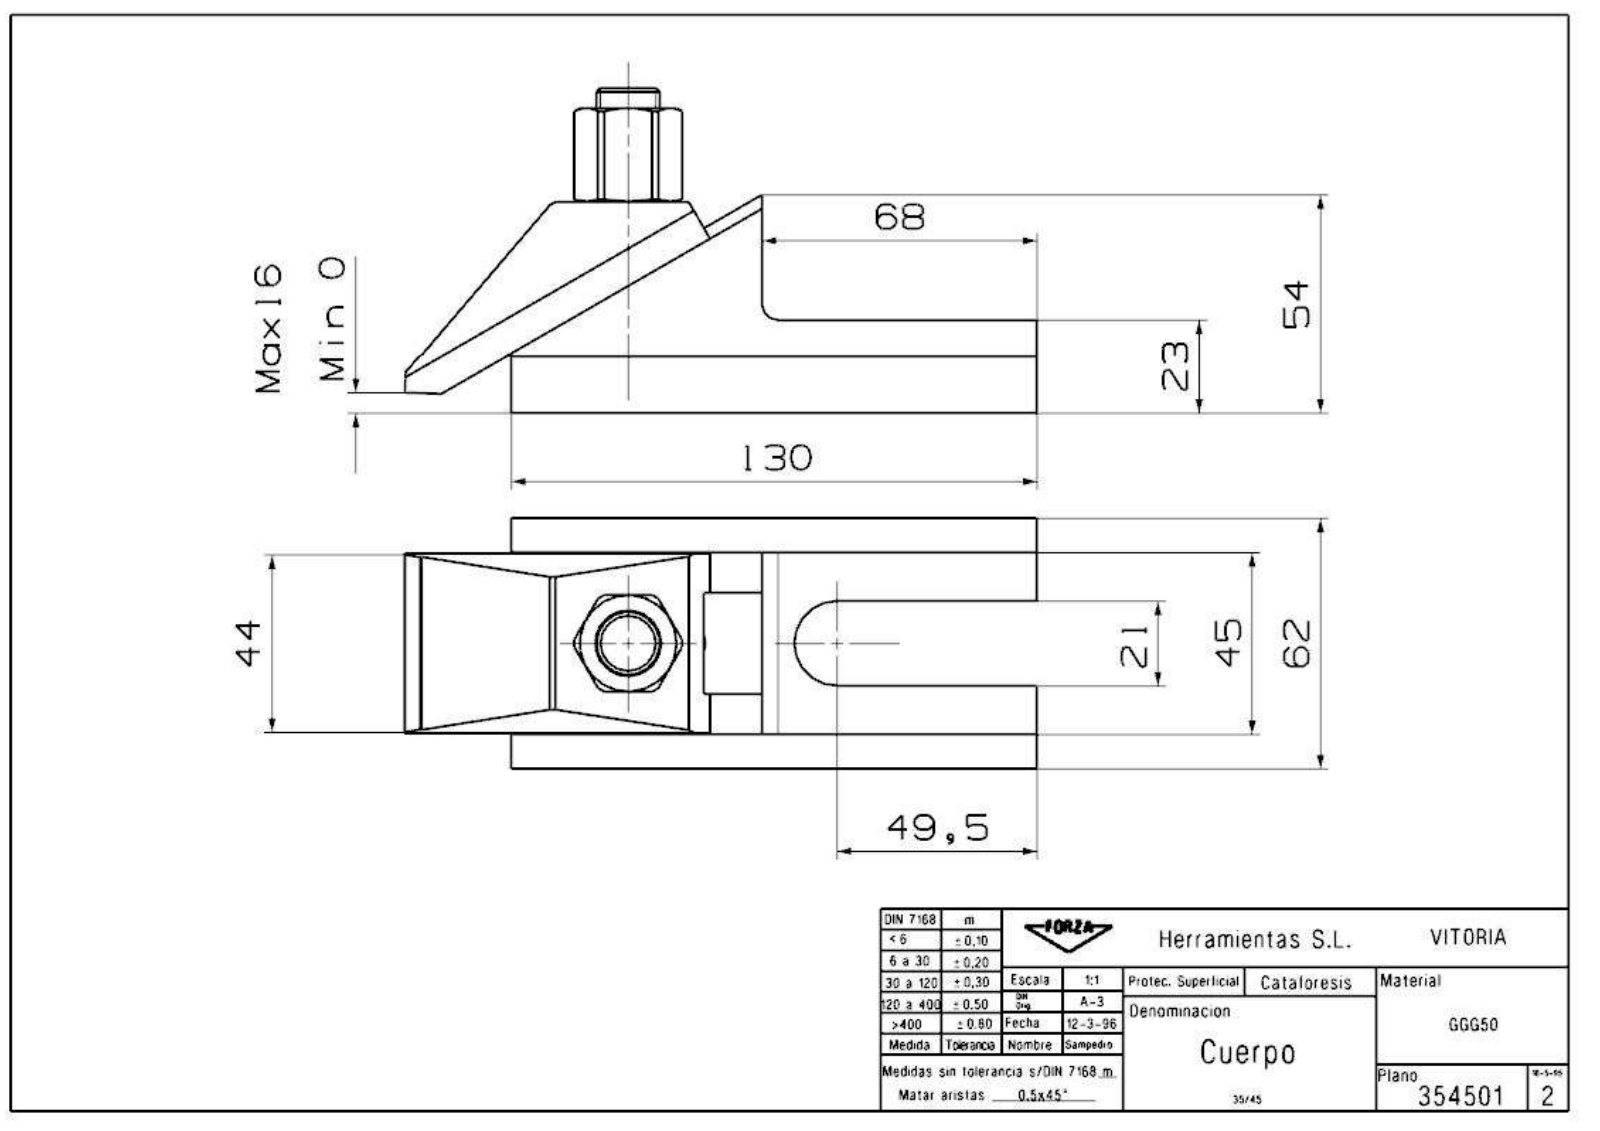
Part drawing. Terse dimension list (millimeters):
name: 354500_Mordaza
written by: SIEMENS PLM Software NX 9.0 (CONFIG_CONTROL_DESIGN)
unit: mm
bodies: 5 solids, 128 faces (91 planar, 22 cylindrical, 15 other)
size: 156.4 × 80.41 × 62
volume: 216 963 mm³; area: 52 137 mm²
holes: 1× ⌀14.38, 1× ⌀18.5, 1× ⌀19
bosses: 1× ⌀28, 1× ⌀15.68
rounds: 3× R2, 2× R3, 2× R8.5, 1× R4, 1× R10.5, 1× R13.37, 1× R16.97
face distances: 8.5, 53.5, 14, 12, 2, 20.5, 23, 62, 41.5, 33
